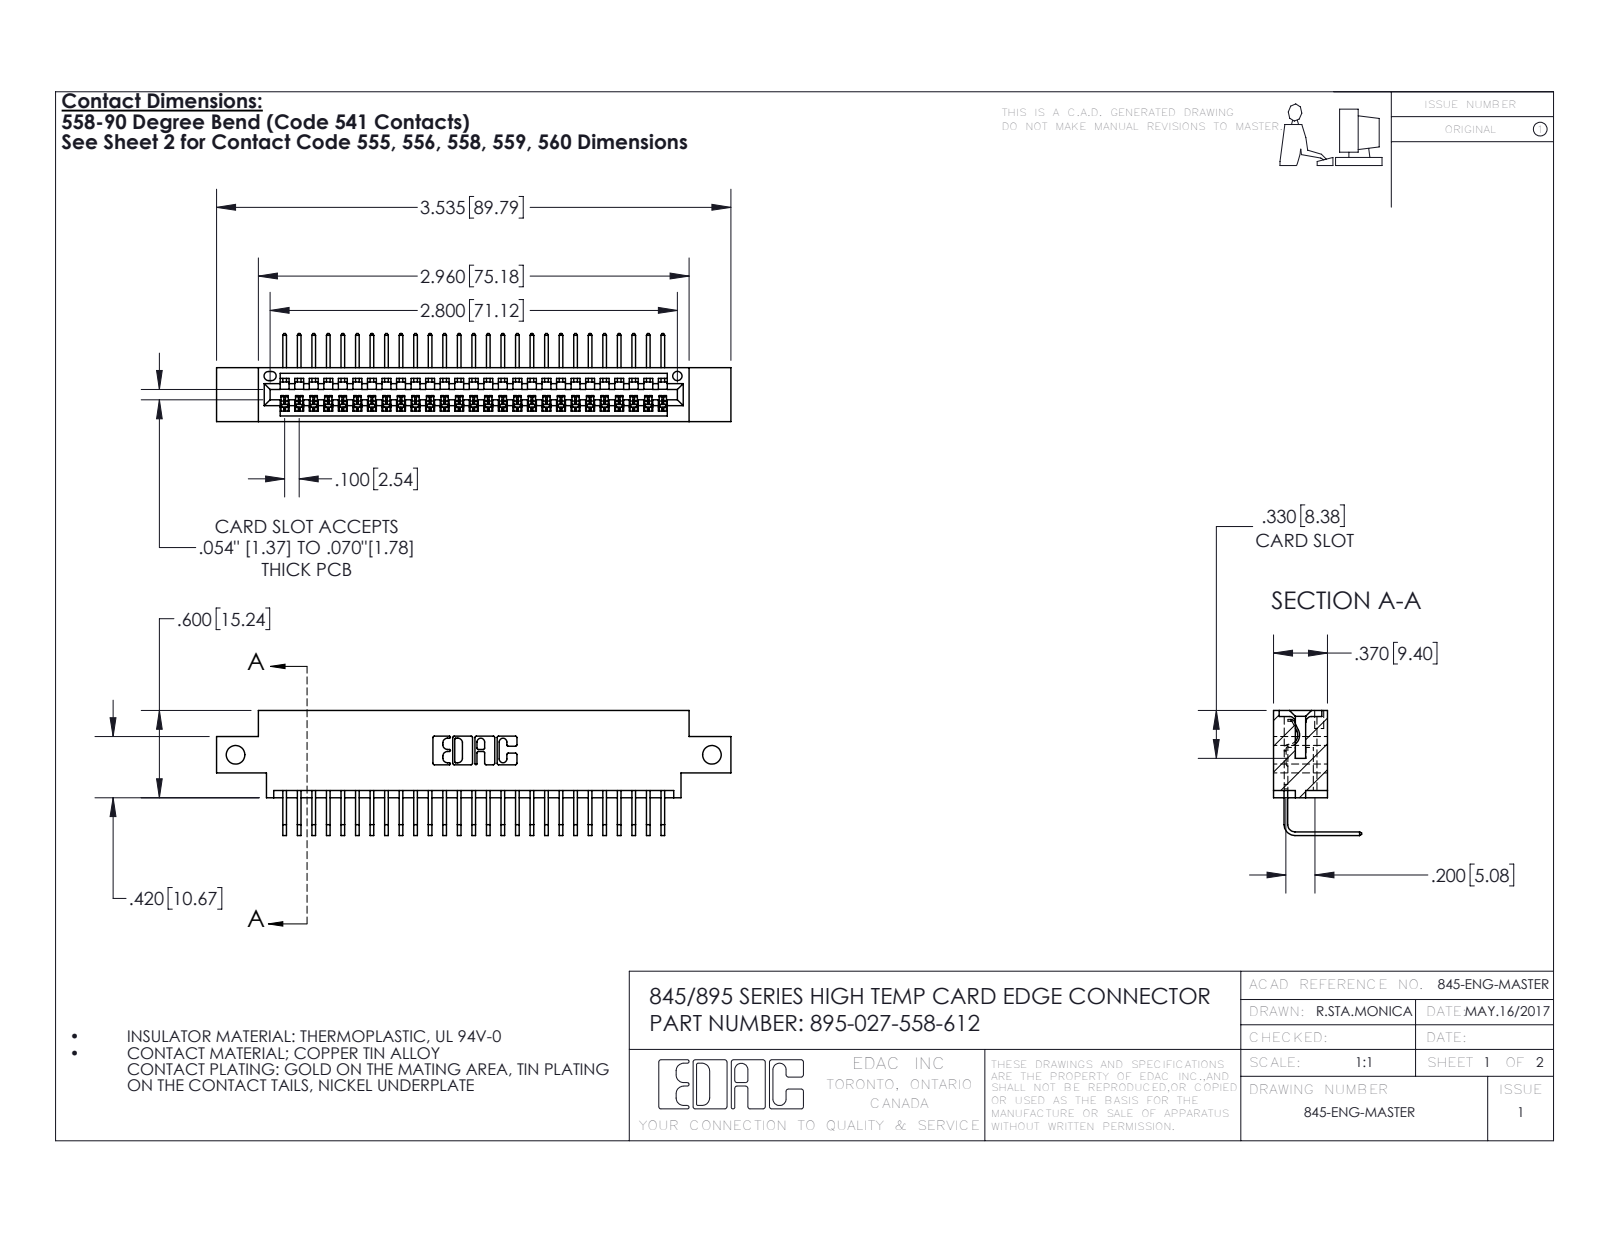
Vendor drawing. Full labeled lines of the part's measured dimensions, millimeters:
Part name (STEP PRODUCT): 395-027-558-612; 345-292-001_558 Tail - 2; 345 Part_0.170 Offset - Side Mount
STEP written by: SolidWorks 2016 (CONFIG_CONTROL_DESIGN)
Units: millimetres
Bodies: 28 solids, 1750 faces (1218 planar, 532 cylindrical, 0 other)
Overall size (bounding box): 89.8 × 21.8 × 15.4
Volume: 8 290 mm³ · Surface area: 11 330 mm²
Round holes (diameter × count): ⌀3.3 ×2, ⌀1.6 ×1
Partial cylindrical surfaces — rounded edges, fillets, slot ends (radius × count): R0.2 ×54, R0.3 ×22, R0.2 ×6, R0.8 ×6, R0.7 ×3, R0.8 ×2, R1 ×2, R0.4 ×1
Main face-to-face distances: 1.8, 7.6, 9.4, 5.1, 2.5, 6.9, 0.6, 5.7, 4.4, 3.8
Hole centre spacings: 83.2
